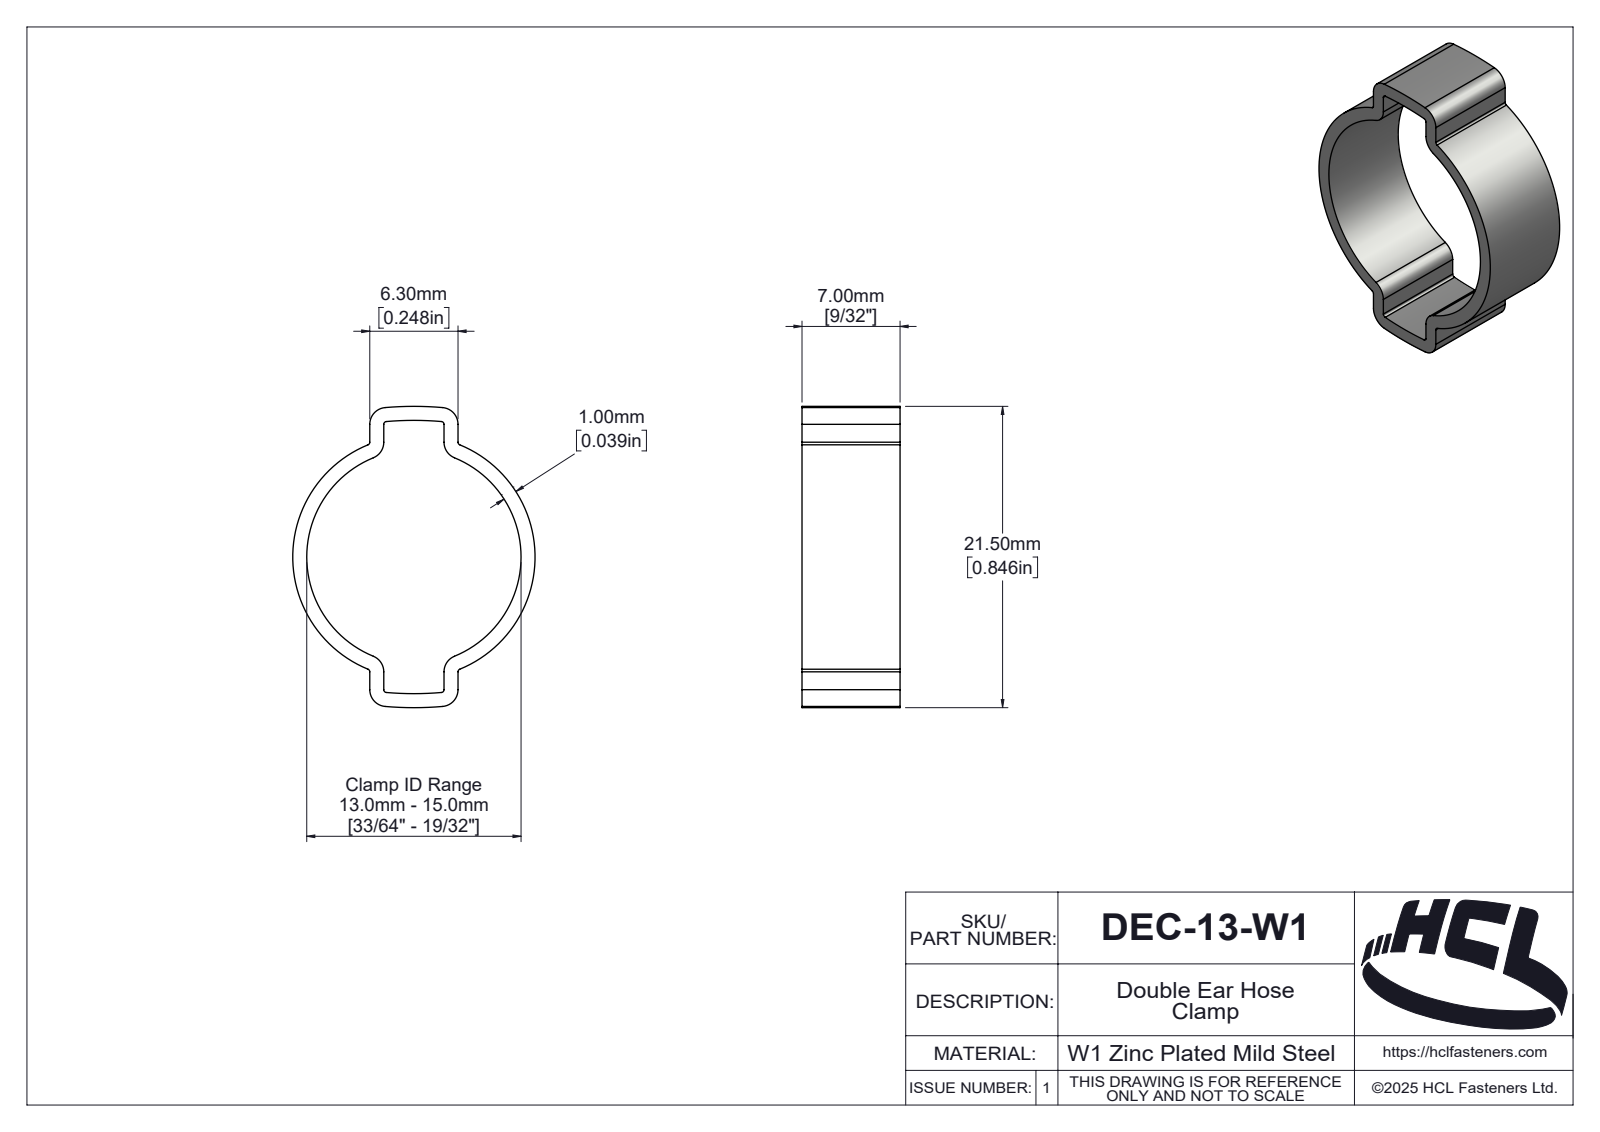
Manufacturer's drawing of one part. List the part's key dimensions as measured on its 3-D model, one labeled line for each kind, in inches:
Part name (STEP PRODUCT): DEC-13-W1
STEP written by: SolidWorks 2025 (AUTOMOTIVE_DESIGN)
Units: inches
Bodies: 1 solid, 137 faces (12 planar, 76 cylindrical, 49 other)
Overall size (bounding box): 0.846 × 0.681 × 0.276
Volume: 0.025 in³ · Surface area: 1.47 in²
Partial cylindrical surfaces — rounded edges, fillets, slot ends (radius × count): R0.008 ×8, R0.047 ×8, R0.912 ×2, R0.951 ×2, R0.005 ×1, R0.021 ×1, R0.026 ×1, R0.028 ×1
Main face-to-face distances: 0.276, 0.039, 0.209, 0.248, 0.169, 0.117, 0.078, 0.092, 0.131, 0.121
